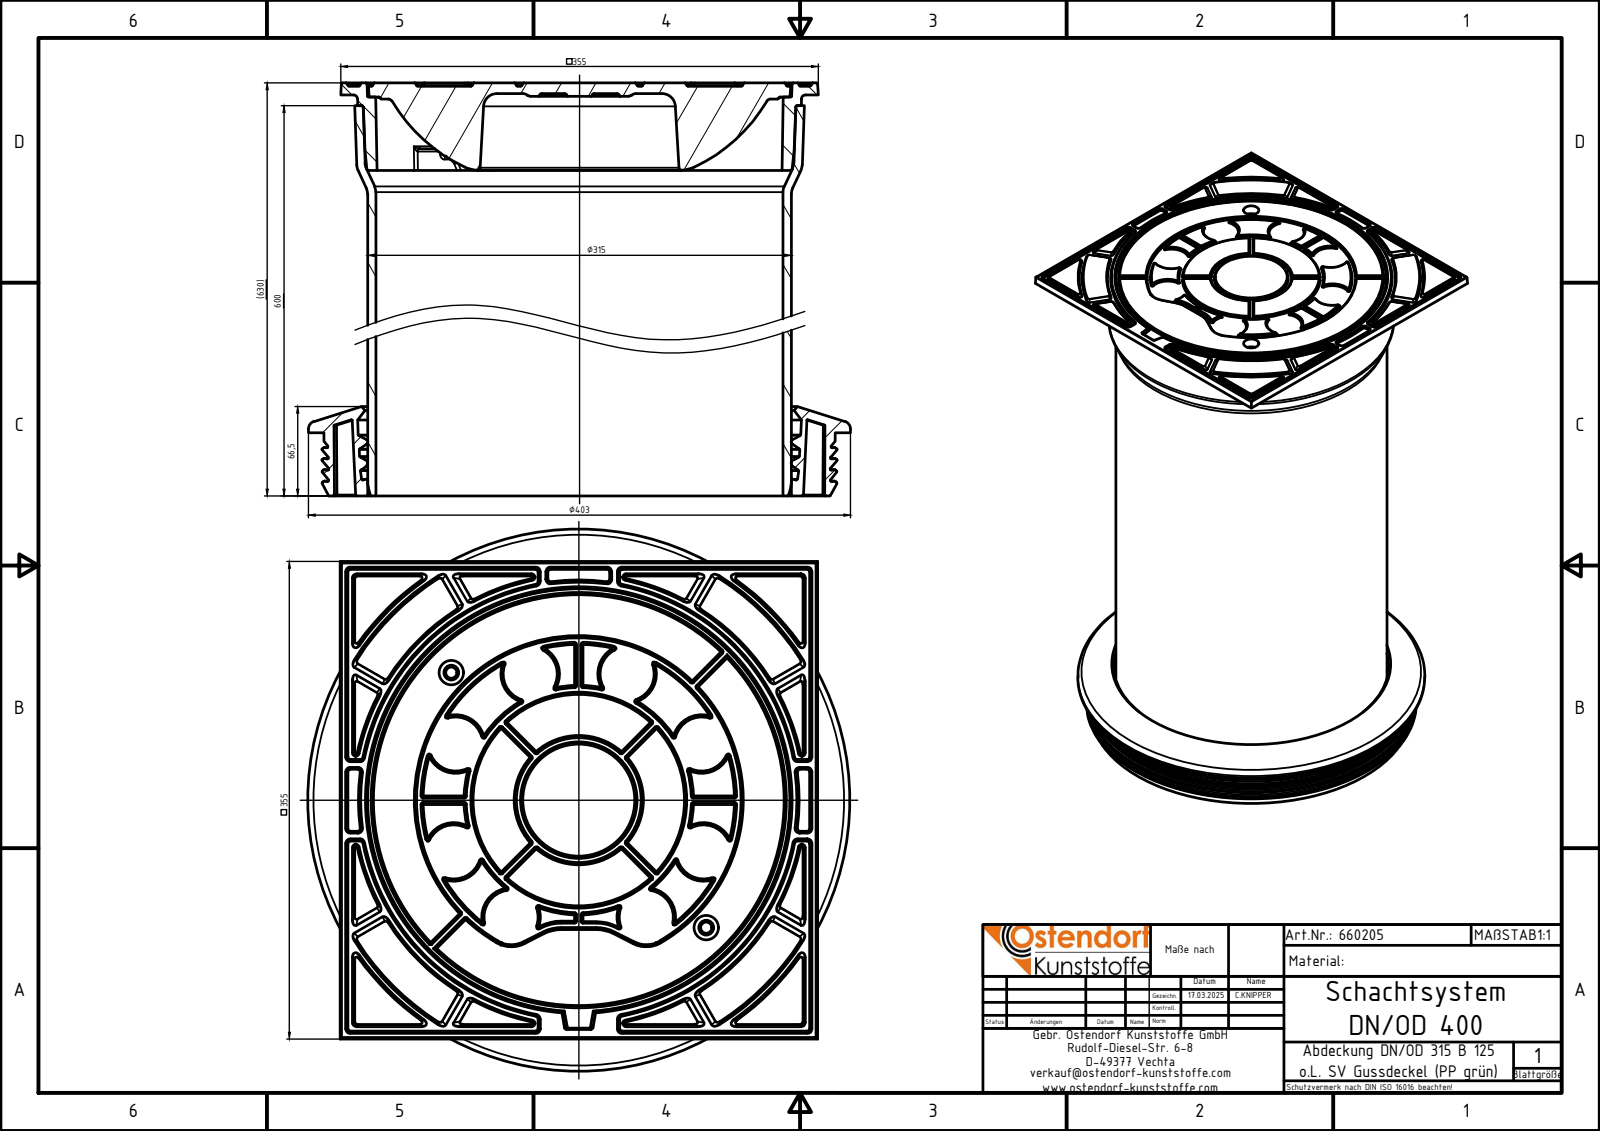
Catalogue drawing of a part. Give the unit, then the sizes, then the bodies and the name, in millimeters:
Units: millimetres
Overall size (bounding box): 617 × 403 × 403
Round holes (diameter × count): ⌀8.38 ×2, ⌀11 ×2, ⌀18 ×2, ⌀302.6 ×1, ⌀315 ×1
Round bosses / shafts (diameter × count): ⌀403 ×1, ⌀380 ×1, ⌀330 ×1
Partial cylindrical surfaces — rounded edges, fillets, slot ends (radius × count): R1 ×153, R2 ×8, R2.5 ×8
Main face-to-face distances: 9, 2.5, 6.5, 8, 608, 614.5, 617, 1.5, 47, 561
Hole centre spacings: 134, 267.99
Volume: 8 130 000 mm³ · Surface area: 2 042 000 mm²
Bodies: 4 solids, 1501 faces (200 planar, 241 cylindrical, 1060 other)
Part name (STEP PRODUCT): 660205z; 660205_Dichtungz; 990010_1z; 990010_2z (+1 more)
STEP written by: Autodesk Inventor 2024 (AUTOMOTIVE_DESIGN)
